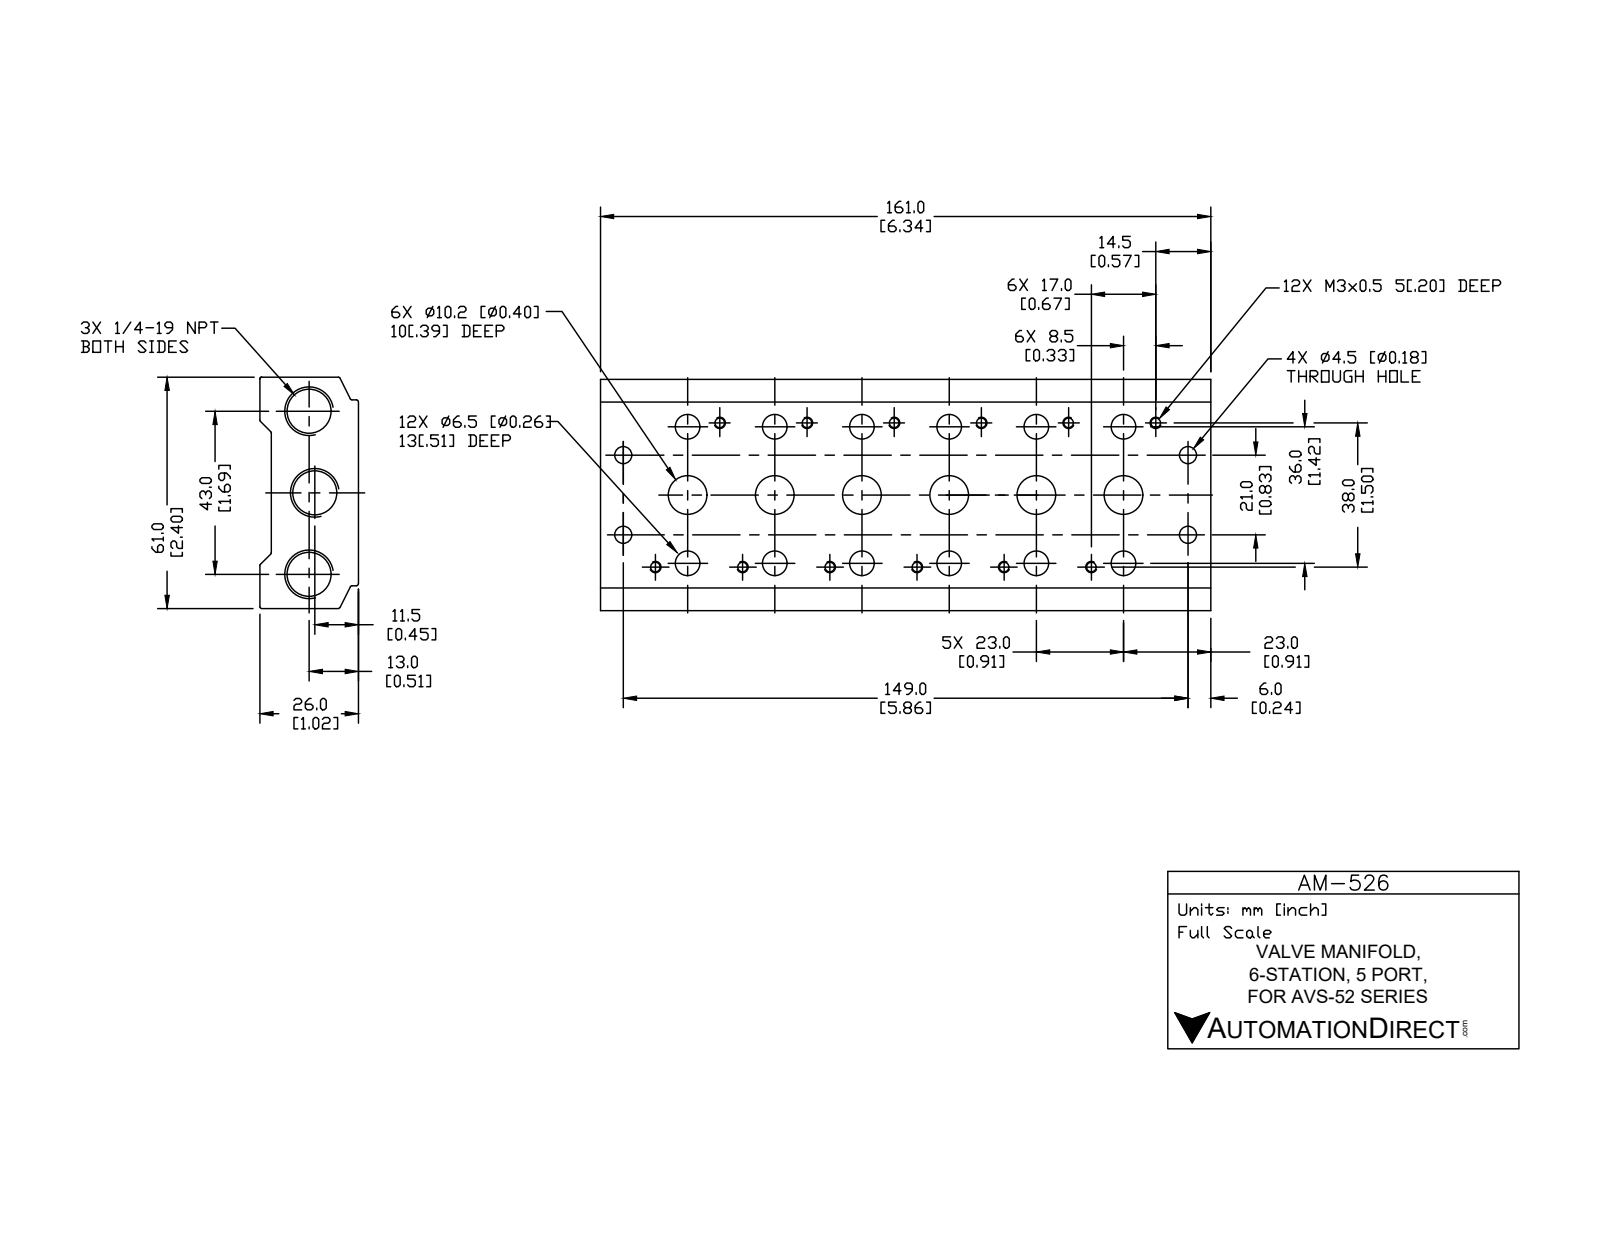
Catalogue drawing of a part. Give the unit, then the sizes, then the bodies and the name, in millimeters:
Units: millimetres
Overall size (bounding box): 161 × 61 × 26
Round holes (diameter × count): ⌀2.5 ×12, ⌀6.5 ×12, ⌀10.2 ×6, ⌀4.5 ×4, ⌀11.13 ×3
Partial cylindrical surfaces — rounded edges, fillets, slot ends (radius × count): R0.5 ×11
Main face-to-face distances: 23, 61, 3, 26, 161, 6, 55, 10.02, 150.98, 49
Hole centre spacings: 23, 29.21, 46, 69, 8.56, 18, 20.81, 37.96
Volume: 175 370 mm³ · Surface area: 51 011 mm²
Bodies: 1 solid, 153 faces (32 planar, 85 cylindrical, 36 other)
Part name (STEP PRODUCT): AM-526
STEP written by: SolidWorks 2015 (CONFIG_CONTROL_DESIGN)
